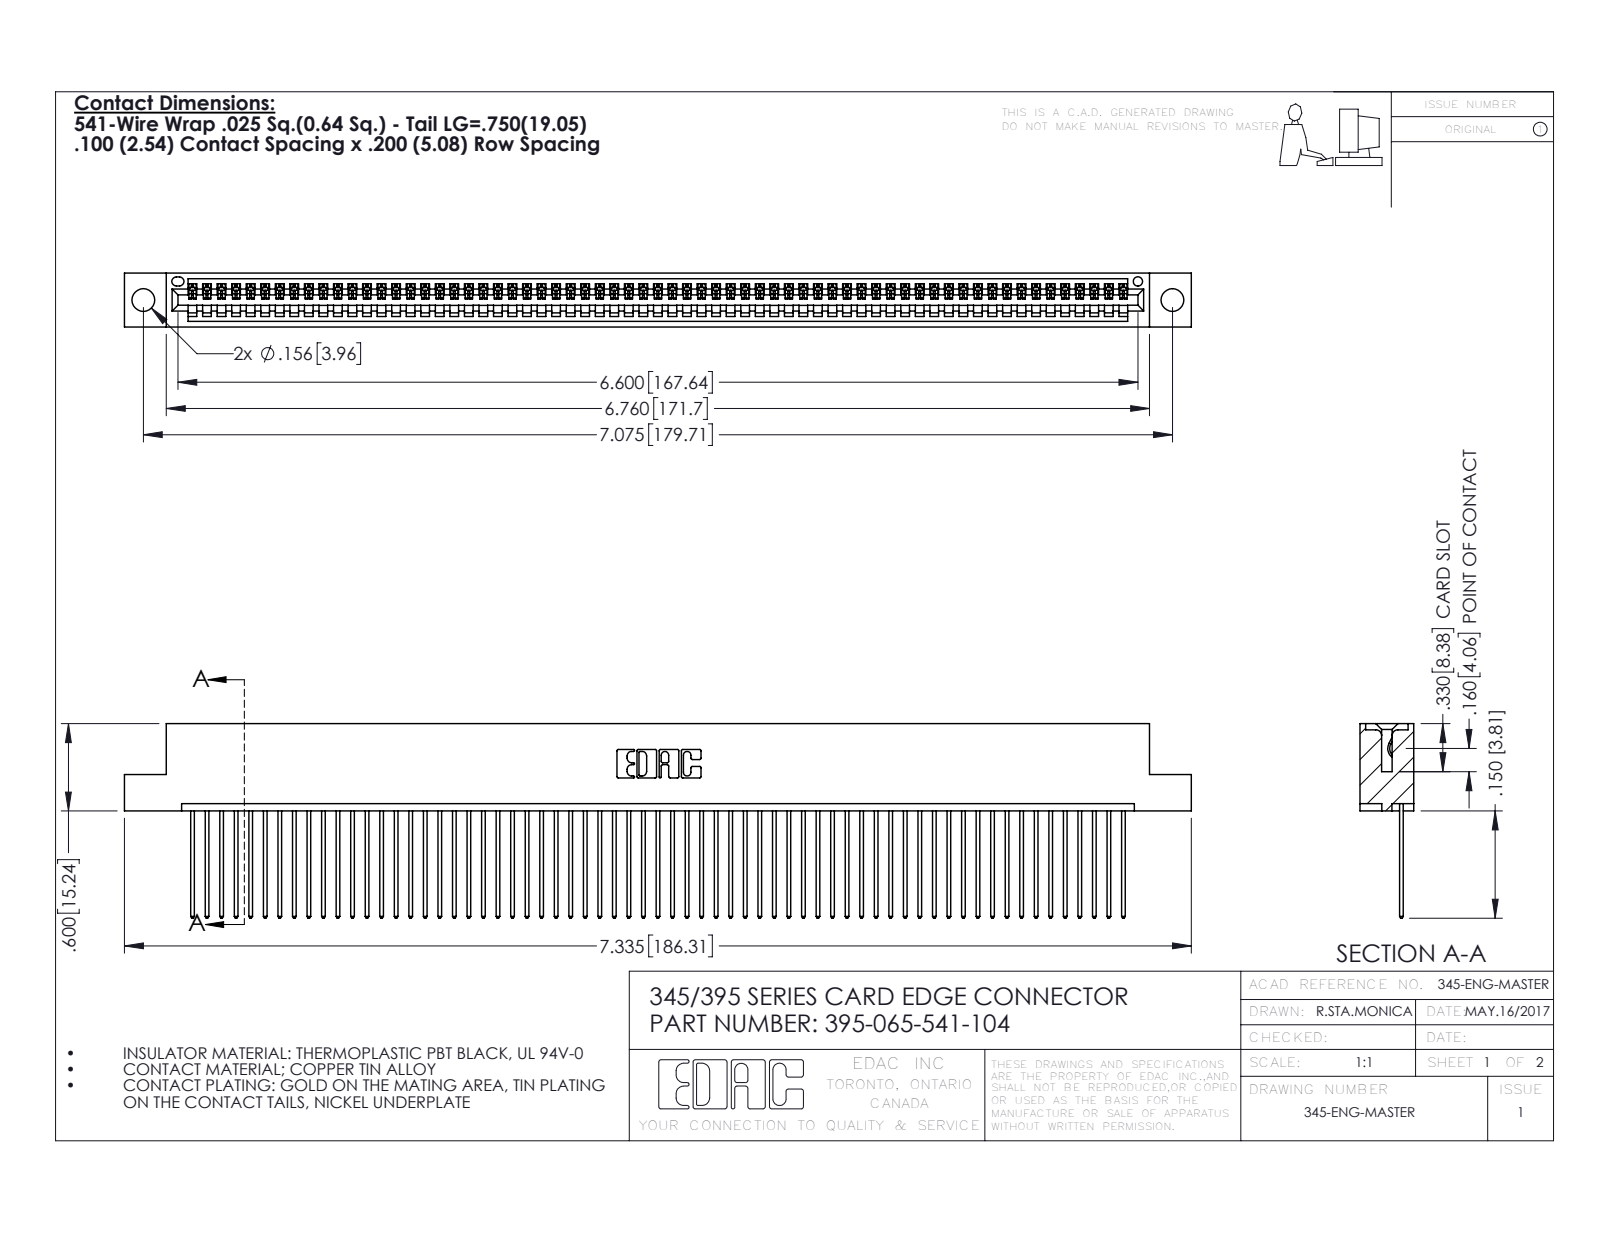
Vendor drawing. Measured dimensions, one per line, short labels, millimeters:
name: 345 Part_Flush Mounting Lugs - 0.156 Dia-TH; 395-065-541-104; 345-292-001_345-293-141
written by: SolidWorks 2016 (CONFIG_CONTROL_DESIGN)
unit: mm
bodies: 66 solids, 3896 faces (2680 planar, 1216 cylindrical, 0 other)
size: 186.3 × 34 × 9.4
volume: 18 010 mm³; area: 25 320 mm²
holes: 2× ⌀4, 1× ⌀1.6
rounds: 130× R0.2, 130× R0.3, 22× R0.3, 6× R0.2, 6× R0.8, 3× R0.7, 2× R0.8, 2× R1
face distances: 1.8, 7.6, 2.5, 6.9, 0.6, 9.4, 5.1, 5.7, 3.8, 1.8
hole spacings: 6.9, 173.7, 179.7
